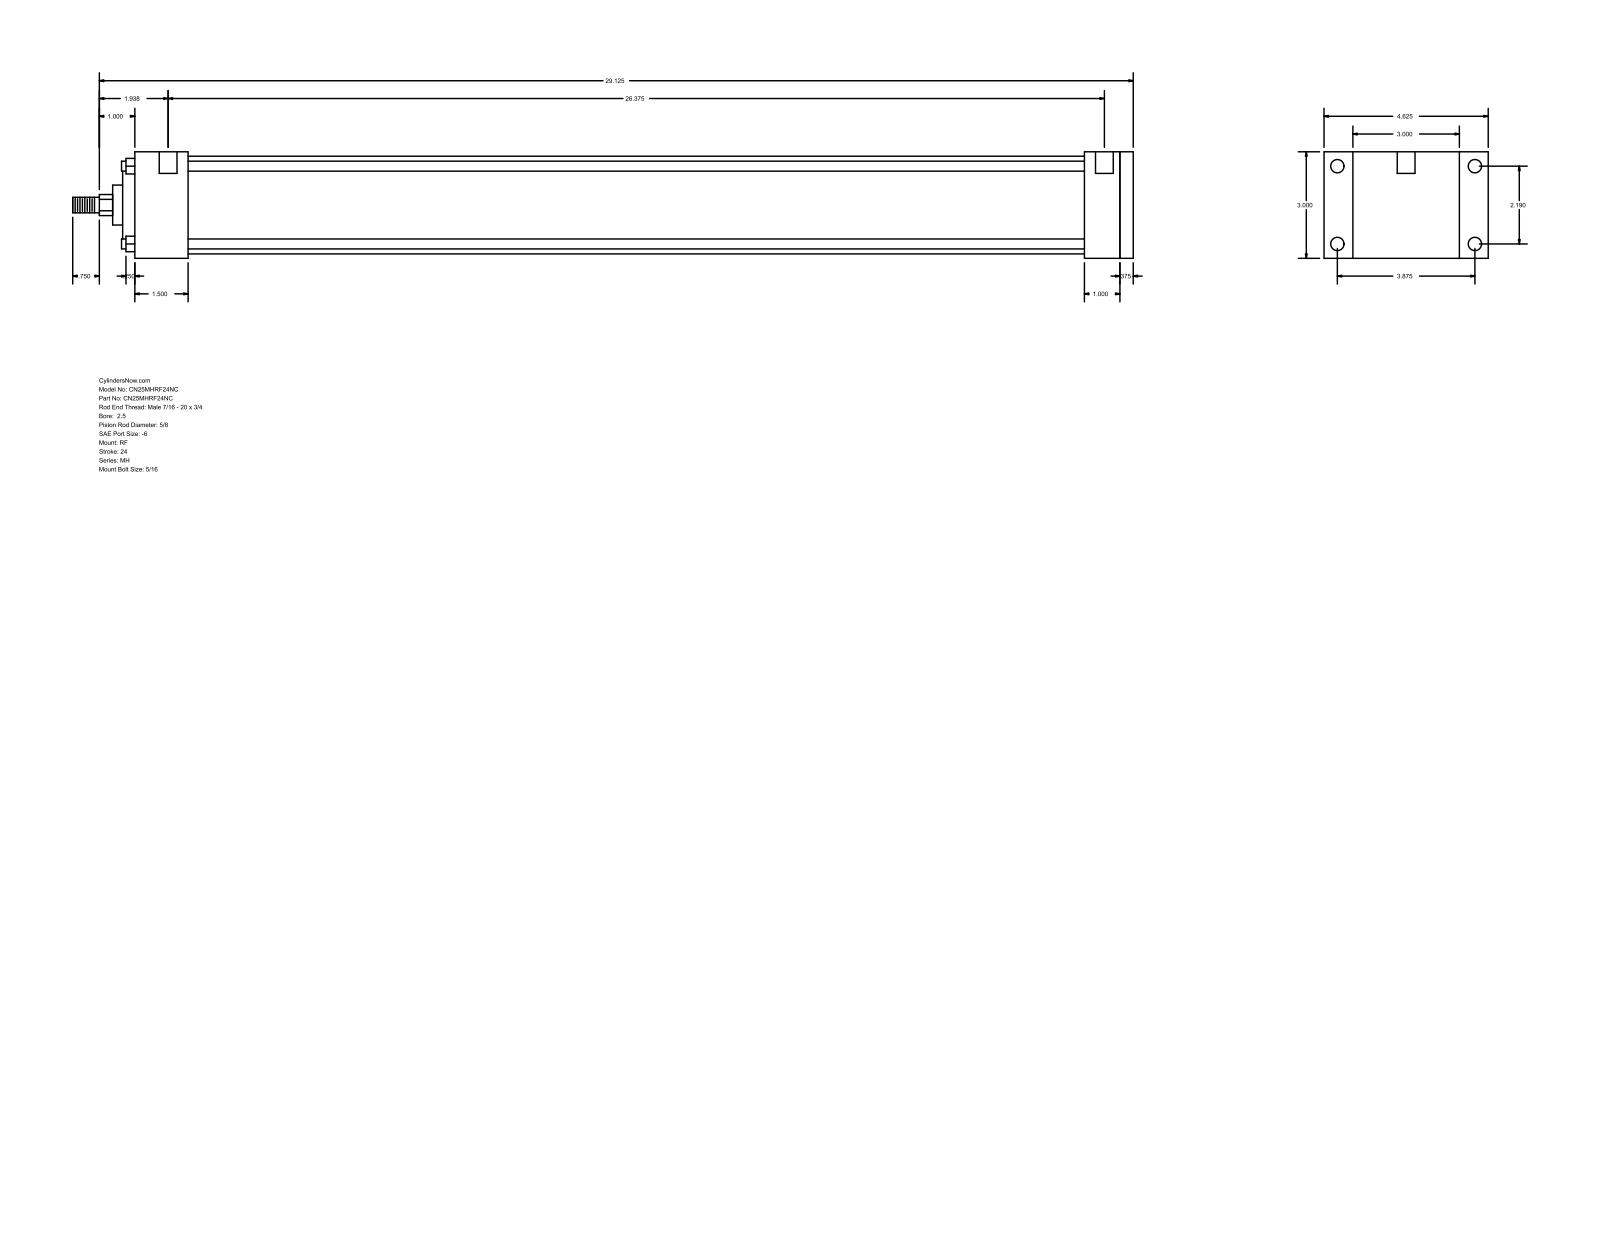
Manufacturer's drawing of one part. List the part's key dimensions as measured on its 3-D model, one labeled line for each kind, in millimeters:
Part name (STEP PRODUCT): MH_RF__0250_0.625
STEP written by: GSSL Pune (CONFIG_CONTROL_DESIGN)
Units: millimetres
Bodies: 0 solids, 94 faces (65 planar, 29 cylindrical, 0 other)
Overall size (bounding box): 758.83 × 117.47 × 76.2
Round holes (diameter × count): ⌀5.56 ×4, ⌀9.53 ×4, ⌀12.7 ×2
Round bosses / shafts (diameter × count): ⌀7.14 ×4, ⌀69.85 ×1, ⌀55.55 ×1, ⌀28.57 ×1, ⌀15.88 ×1, ⌀11.11 ×1
Partial cylindrical surfaces — rounded edges, fillets, slot ends (radius × count): R7.54 ×1
Main face-to-face distances: 76.2, 9.52, 714.37, 704.85, 25.4, 38.1, 679.45, 34.92, 641.35, 666.75
Hole centre spacings: 55.62, 98.42, 113.05, 677.86, 3.17, 4.76, 669.93, 673.1
